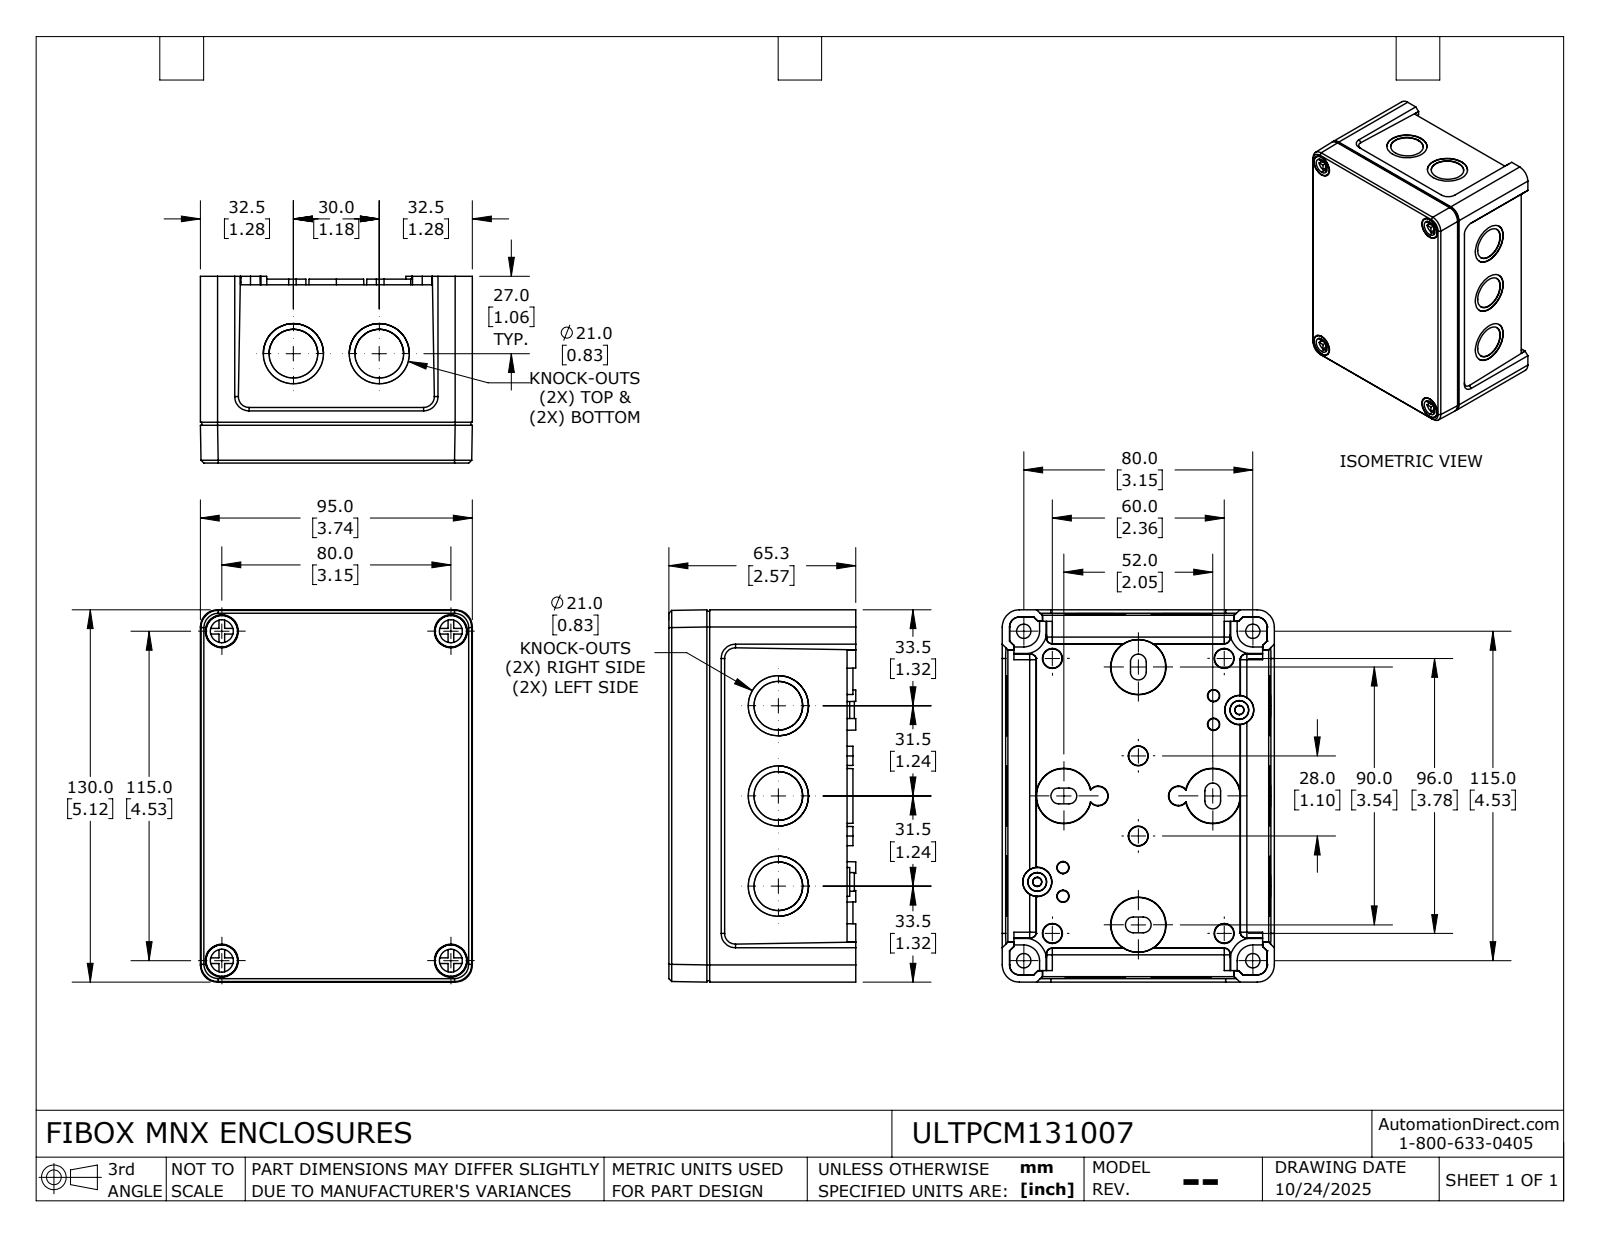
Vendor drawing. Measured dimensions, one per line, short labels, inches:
name: ULTPCM131007_Default
written by: SolidWorks 2024 (CONFIG_CONTROL_DESIGN)
unit: in
bodies: 6 solids, 706 faces (360 planar, 194 cylindrical, 152 other)
size: 5.118 × 3.74 × 2.569
volume: 9.402 in³; area: 189.8 in²
holes: 12× ⌀0.827, 10× ⌀0.669, 4× ⌀0.197, 4× ⌀0.315
bosses: 4× ⌀0.433, 4× ⌀0.283
rounds: 24× R0.079, 8× R0.02, 8× R0.039, 8× R0.104, 8× R0.108, 8× R0.236, 4× R0.091, 4× R0.197
face distances: 0.074, 0.108, 0.079, 2.175, 2.067, 2.146, 2.254, 0.197, 0.276, 1.654
hole spacings: 1.24, 1.181, 2.48, 1.273, 2.706, 3.15, 3.509, 4.245
